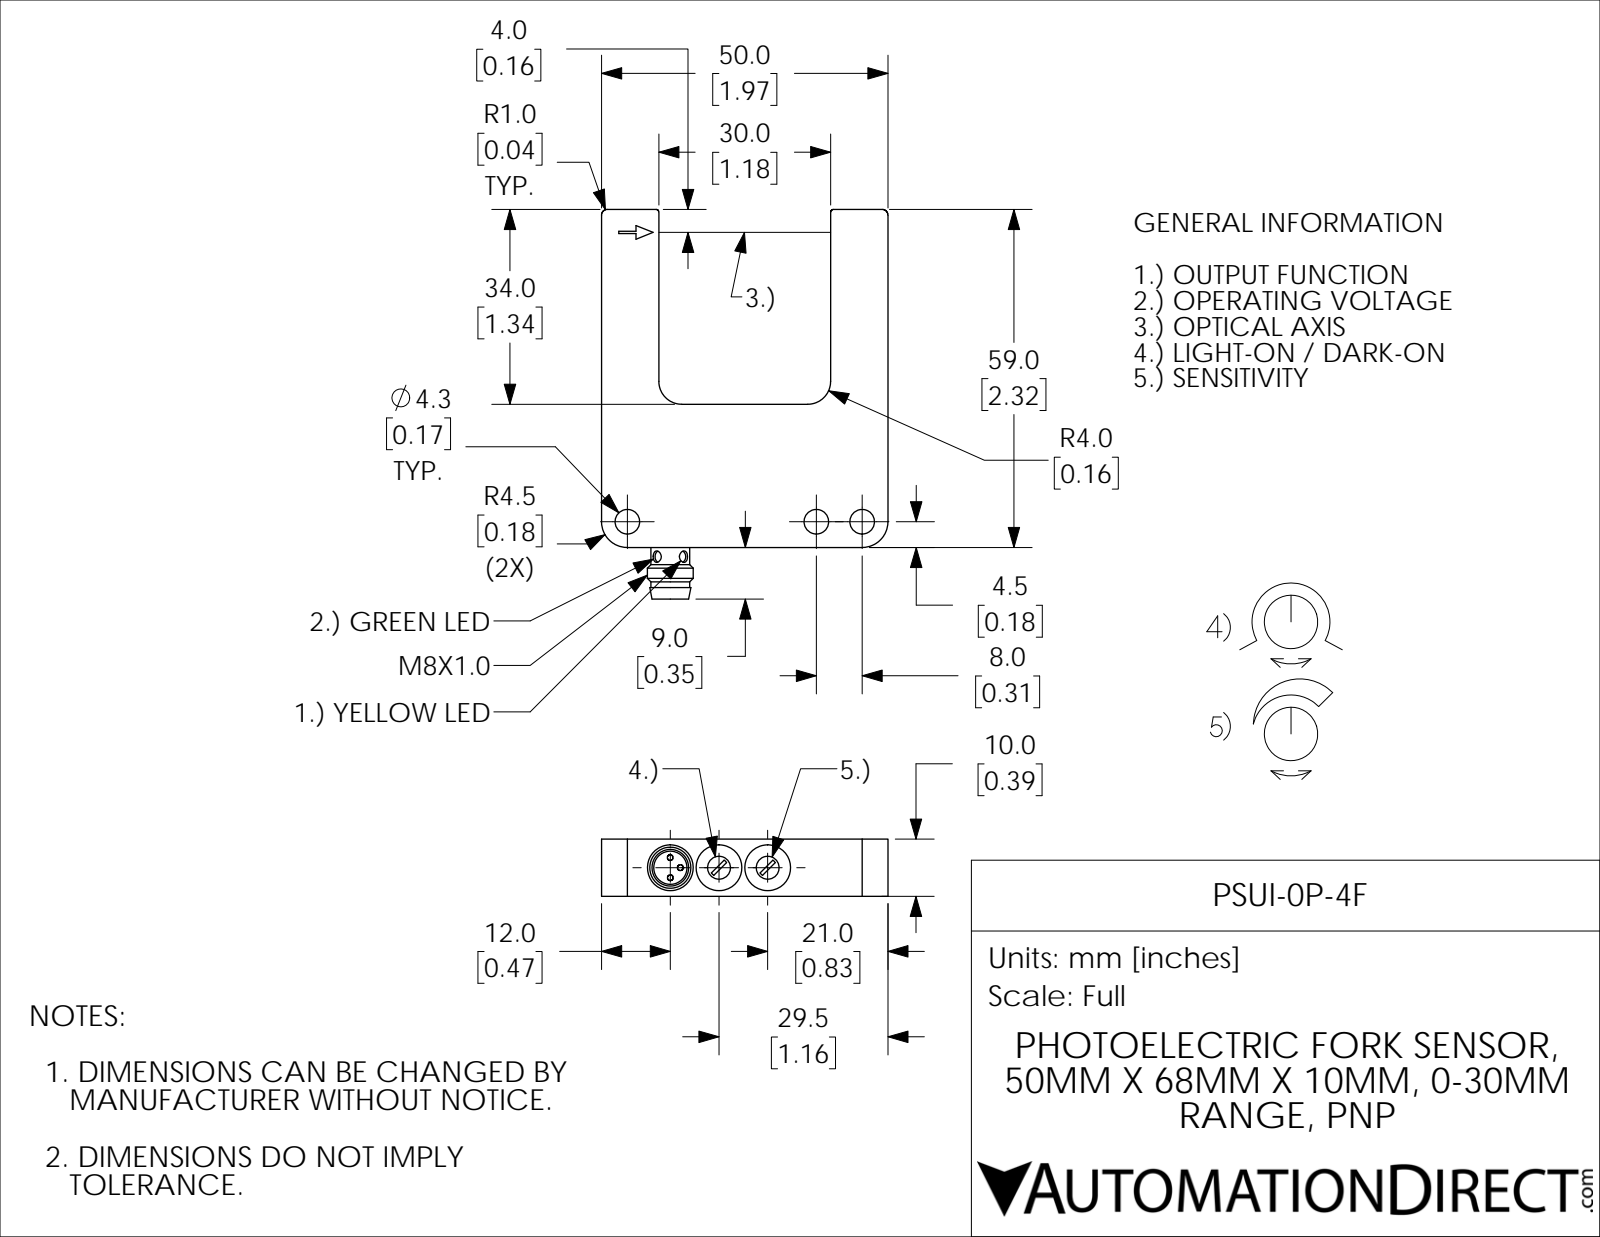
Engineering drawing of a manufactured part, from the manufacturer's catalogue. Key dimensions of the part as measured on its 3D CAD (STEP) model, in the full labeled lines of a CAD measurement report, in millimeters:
Part name (STEP PRODUCT): PSUI-0P-4F
STEP written by: SolidWorks 2017 (AUTOMOTIVE_DESIGN)
Units: millimetres
Bodies: 1 solid, 71 faces (35 planar, 30 cylindrical, 6 other)
Overall size (bounding box): 68 × 50 × 10
Volume: 19 060 mm³ · Surface area: 7 323 mm²
Round holes (diameter × count): ⌀4.3 ×3, ⌀2 ×2, ⌀4 ×2, ⌀8 ×2, ⌀5.8 ×1
Round bosses / shafts (diameter × count): ⌀1 ×3, ⌀8 ×1, ⌀6.8 ×1
Partial cylindrical surfaces — rounded edges, fillets, slot ends (radius × count): R0.5 ×2, R1 ×2, R1.6 ×2, R4 ×2, R4.5 ×2
Main face-to-face distances: 10, 40, 50, 30, 25, 34, 59, 58.9, 24.9, 4
Hole centre spacings: 8.5, 8, 17, 33, 41
